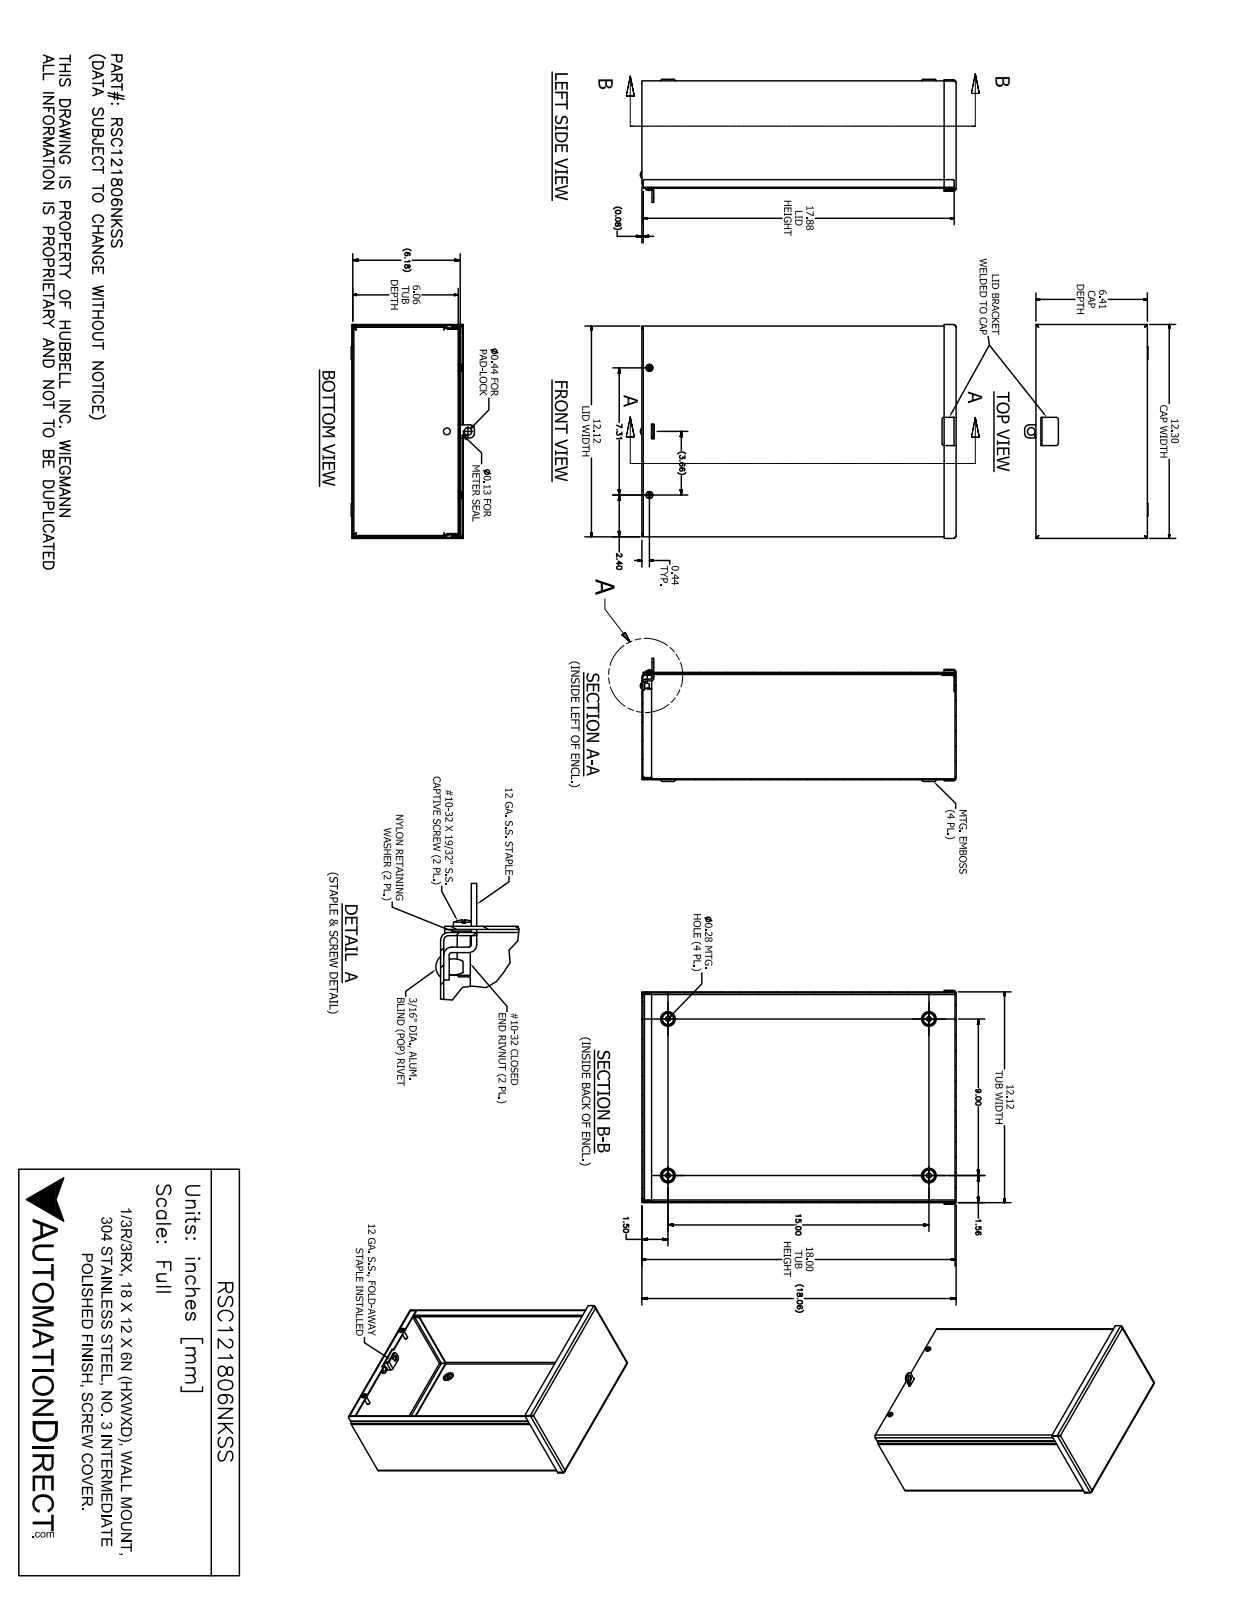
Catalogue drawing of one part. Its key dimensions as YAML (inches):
part_name: "RSC121806NKSSBLR; HFW369104; 39077; 34984 (+7 more)"
step_written_by: "SolidWorks 2017 (AUTOMOTIVE_DESIGN)"
units: inches
bodies: {solids: 13, faces: 383, planar: 199, cylindrical: 99, other: 85}
overall_size: [18.149, 12.299, 7.084]
volume: 50.69
surface_area: 1732
round_holes:
  - {diameter: 0.25, count: 4}
  - {diameter: 0.281, count: 4}
  - {diameter: 0.156, count: 2}
  - {diameter: 0.196, count: 2}
  - {diameter: 0.257, count: 2}
  - {diameter: 0.278, count: 2}
  - {diameter: 0.125, count: 1}
  - {diameter: 0.198, count: 1}
  - {diameter: 0.201, count: 1}
  - {diameter: 0.437, count: 1}
round_bosses_or_shafts:
  - {diameter: 0.453, count: 2}
  - {diameter: 0.406, count: 2}
  - {diameter: 0.248, count: 2}
  - {diameter: 0.167, count: 2}
  - {diameter: 0.187, count: 1}
partial_cylinders:
  - {radius: 0.094, count: 17}
  - {radius: 0.153, count: 17}
  - {radius: 0.031, count: 6}
  - {radius: 0.125, count: 4}
  - {radius: 0.25, count: 4}
  - {radius: 0.047, count: 2}
  - {radius: 0.05, count: 2}
  - {radius: 0.062, count: 2}
face_to_face_distances: [0.059, 6.117, 6.176, 6.058, 12.059, 18, 12, 12.118, 17.941, 18.059]
hole_center_spacings: [1.357, 1.381, 7.313, 8.225, 8.229, 9, 15, 16.085]
